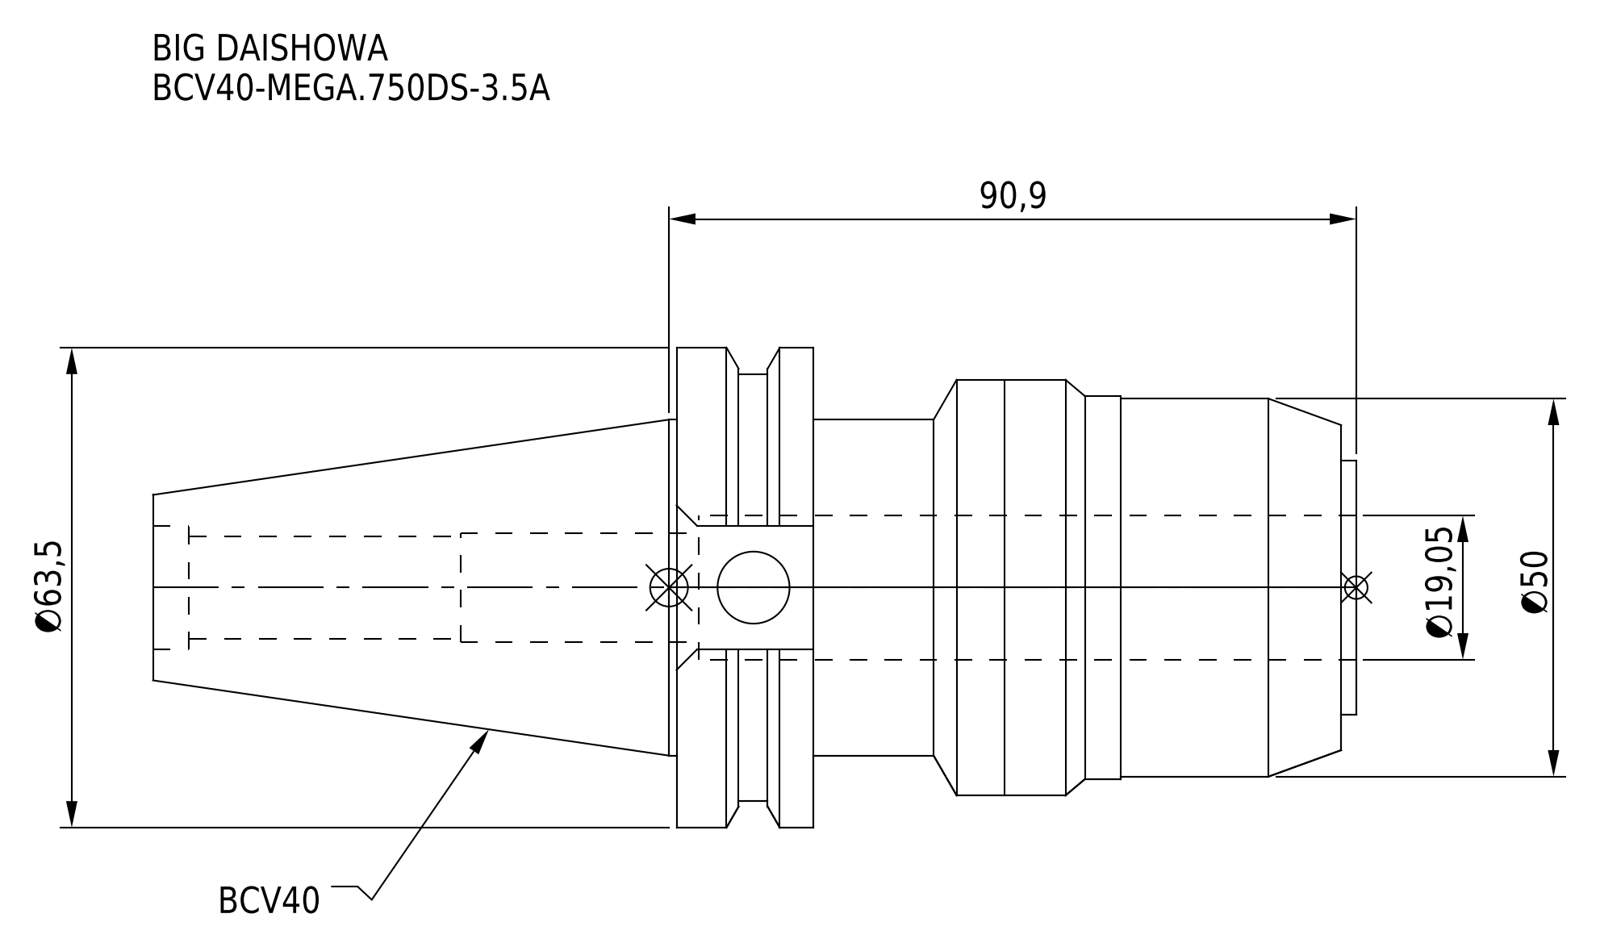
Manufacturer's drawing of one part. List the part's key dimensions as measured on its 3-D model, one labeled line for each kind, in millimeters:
Part name (STEP PRODUCT): BCV40-MEGA_750DS-3_5A
STEP written by: CREO PARAMETRIC BY PTC INC, 2016380 (AUTOMOTIVE_DESIGN)
Units: millimetres
Bodies: 1 solid, 66 faces (24 planar, 30 cylindrical, 12 other)
Overall size (bounding box): 159.15 × 63.5 × 61.35
Volume: 217 187 mm³ · Surface area: 36 812 mm²
Round holes (diameter × count): ⌀9.53 ×1, ⌀13.6 ×1, ⌀14.5 ×1, ⌀16.32 ×1, ⌀19.05 ×1
Round bosses / shafts (diameter × count): ⌀63.5 ×1, ⌀56.36 ×1, ⌀55 ×1, ⌀50.7 ×1, ⌀50 ×1, ⌀44.45 ×1, ⌀33.6 ×1
Main face-to-face distances: 18.05, 71.85, 89.9, 2, 69.85, 87.9, 159.15, 157.15, 87.3, 69.25
